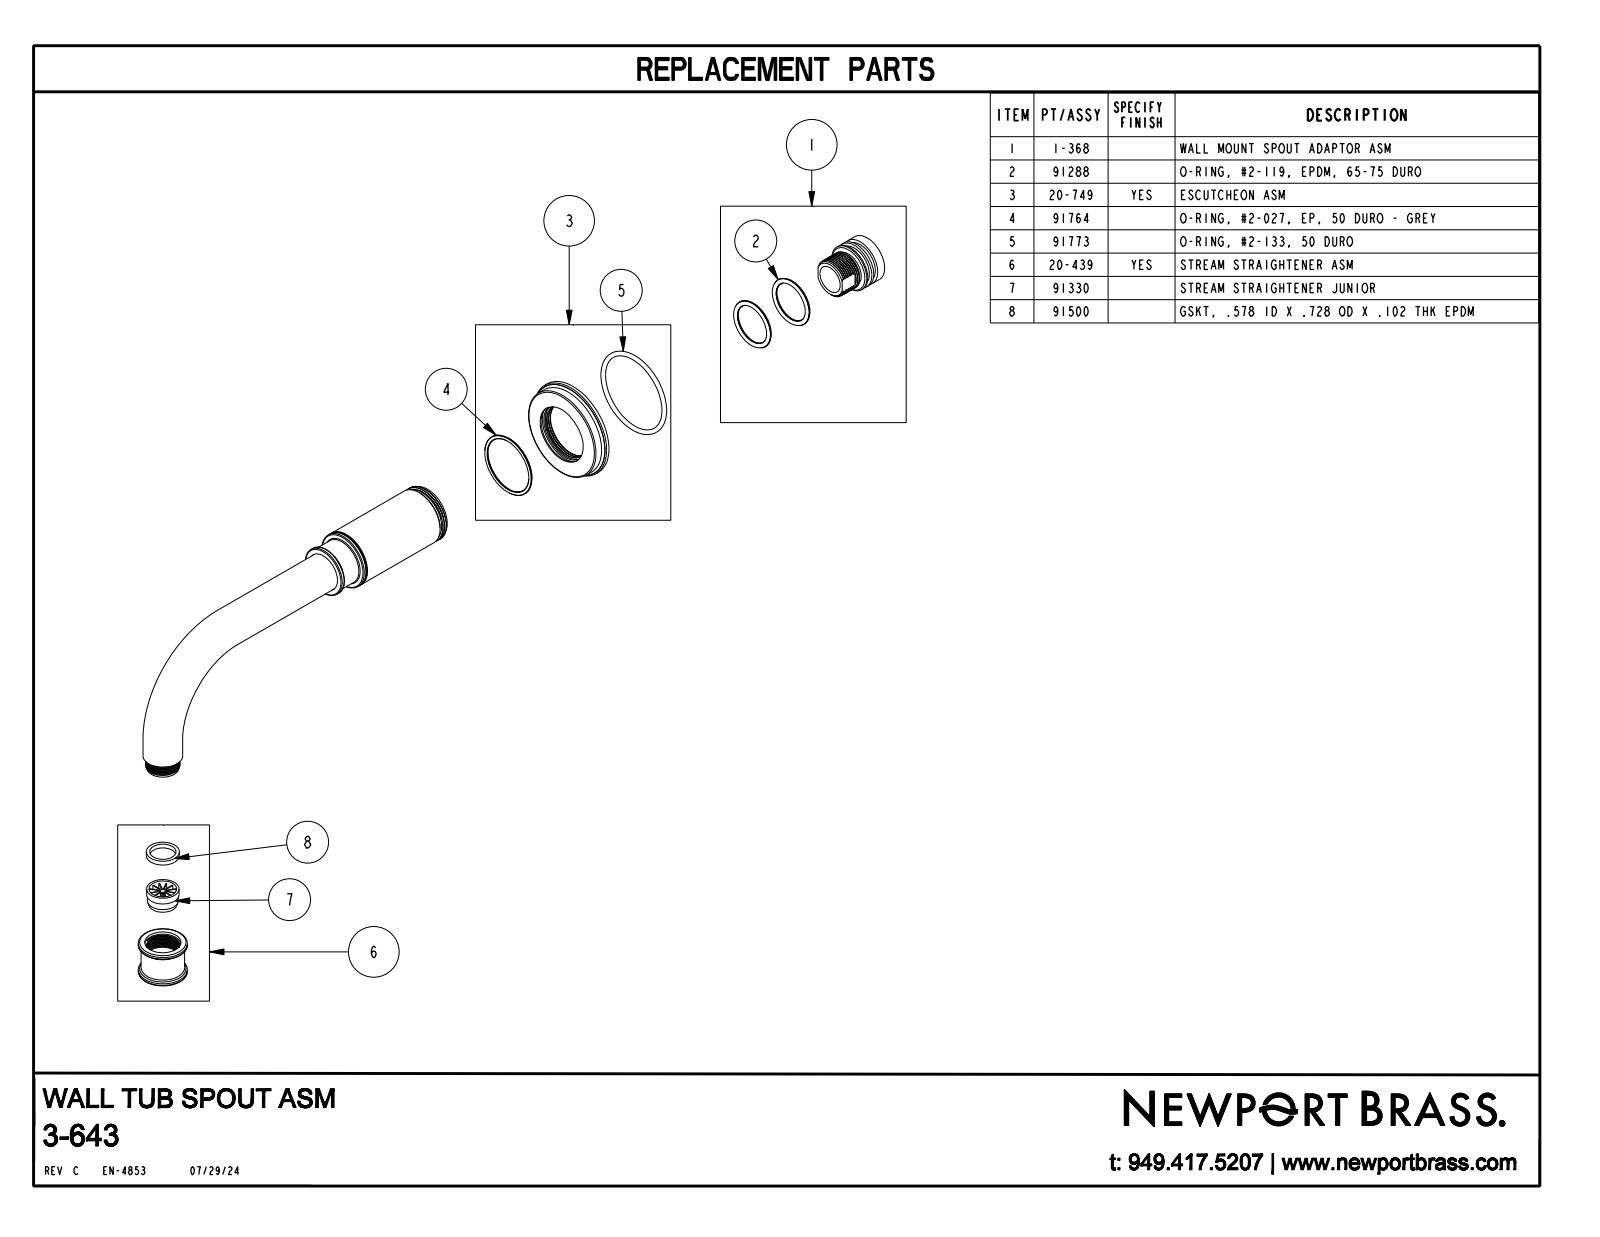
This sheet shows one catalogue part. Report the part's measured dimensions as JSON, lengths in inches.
{"part_name": "3-643", "step_written_by": "CREO PARAMETRIC BY PTC INC, 2019352 (CONFIG_CONTROL_DESIGN)", "units": "inches", "bodies": {"solids": 1, "faces": 153, "planar": 59, "cylindrical": 52, "other": 42}, "overall_size": [8.79, 4.385, 2.25], "volume_in3": 9.476, "surface_area_in2": 43.52, "round_holes": [[0.118, 1], [0.606, 1], [0.691, 1]], "round_bosses_or_shafts": [[0.875, 2], [2.25, 1], [2.09, 1], [1.312, 1], [1.14, 1], [1.08, 1], [1.06, 1], [0.96, 1]], "partial_cylinders_radius": [[0.3, 1]], "face_to_face_distances": [0.35, 3.25, 2.9, 2.65, 2.3, 0.6, 0.06, 0.81, 0.75, 0.04]}
